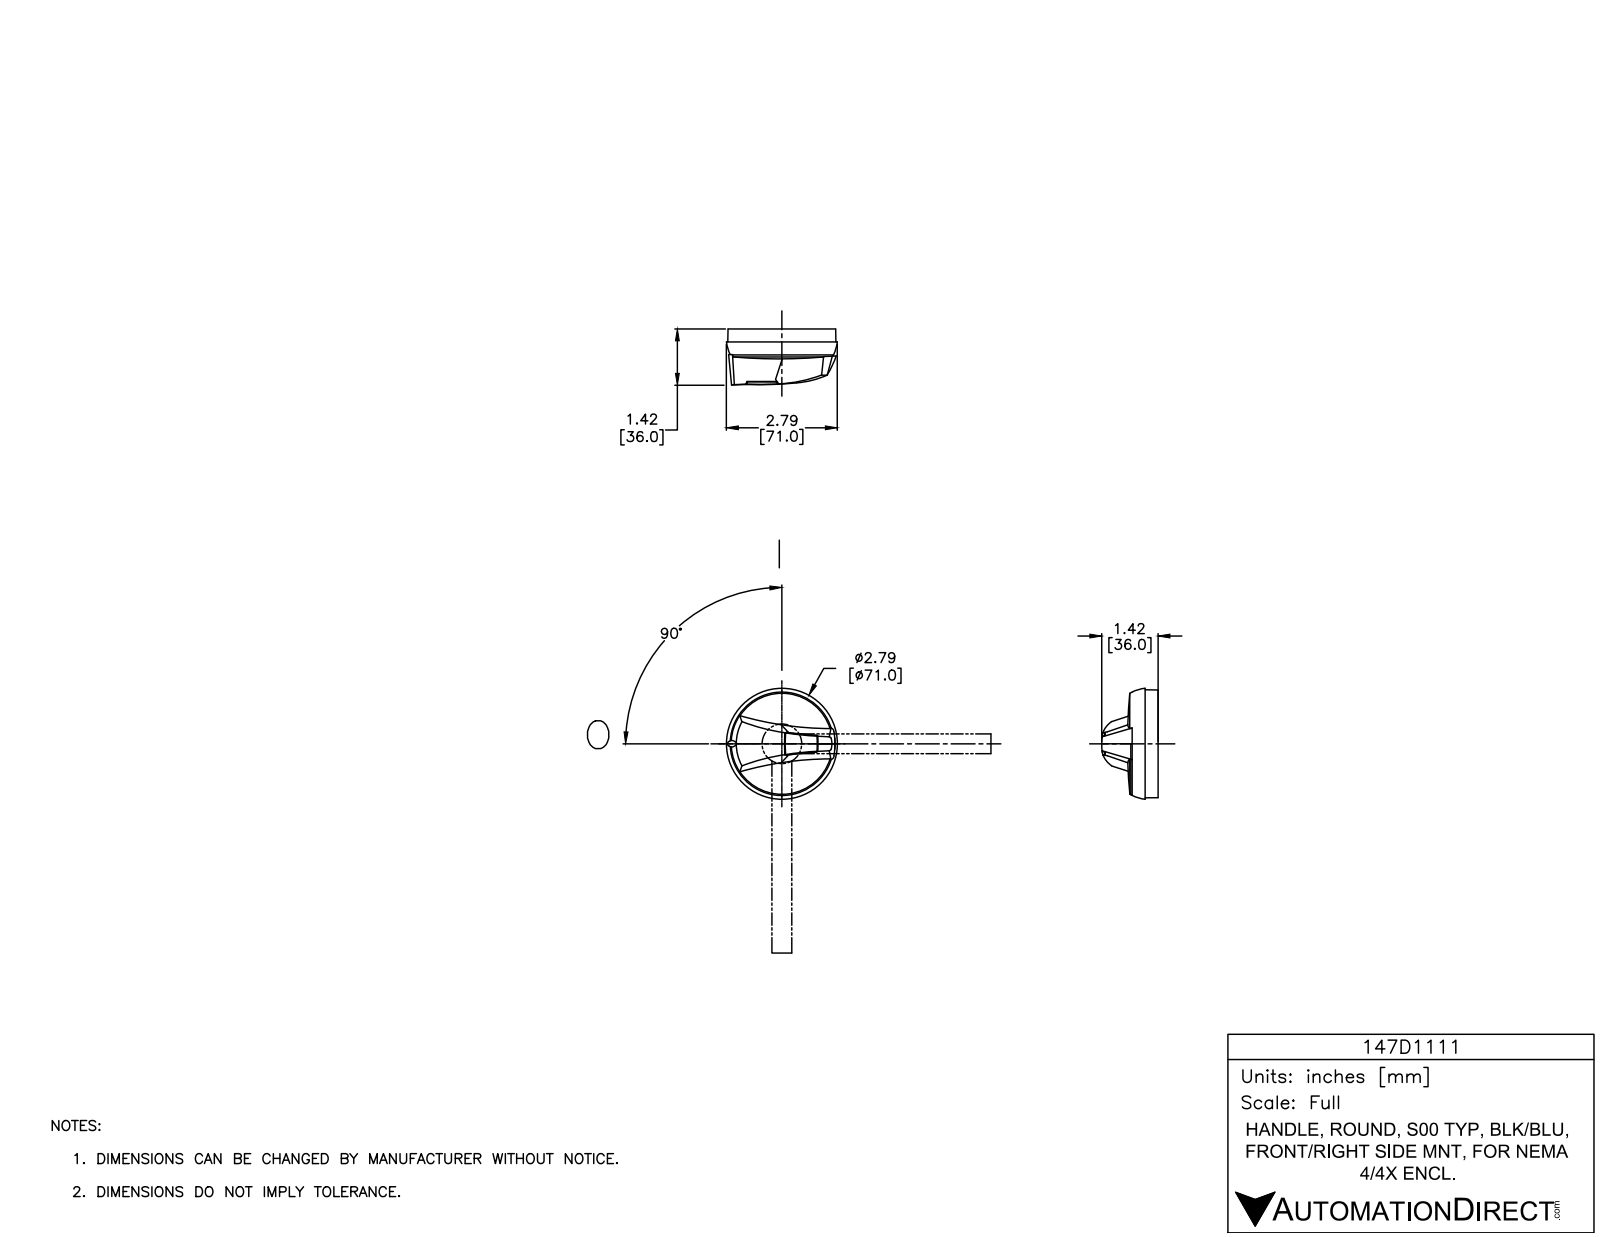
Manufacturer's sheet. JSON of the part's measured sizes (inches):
{"part_name": "147D1111", "step_written_by": "SolidWorks 2015 (AUTOMOTIVE_DESIGN)", "units": "inches", "bodies": {"solids": 1, "faces": 76, "planar": 29, "cylindrical": 14, "other": 33}, "overall_size": [2.8, 2.8, 1.899], "volume_in3": 5.42, "surface_area_in2": 24.86, "round_holes": [[0.169, 4], [0.457, 1], [2.618, 1]], "round_bosses_or_shafts": [[0.801, 1]], "face_to_face_distances": [0.624, 0.616, 0.03, 0.646, 0.654, 0.488, 0.518, 1.134, 1.142, 0.807], "hole_center_spacings": [0.961, 1.102, 1.575, 1.922]}
